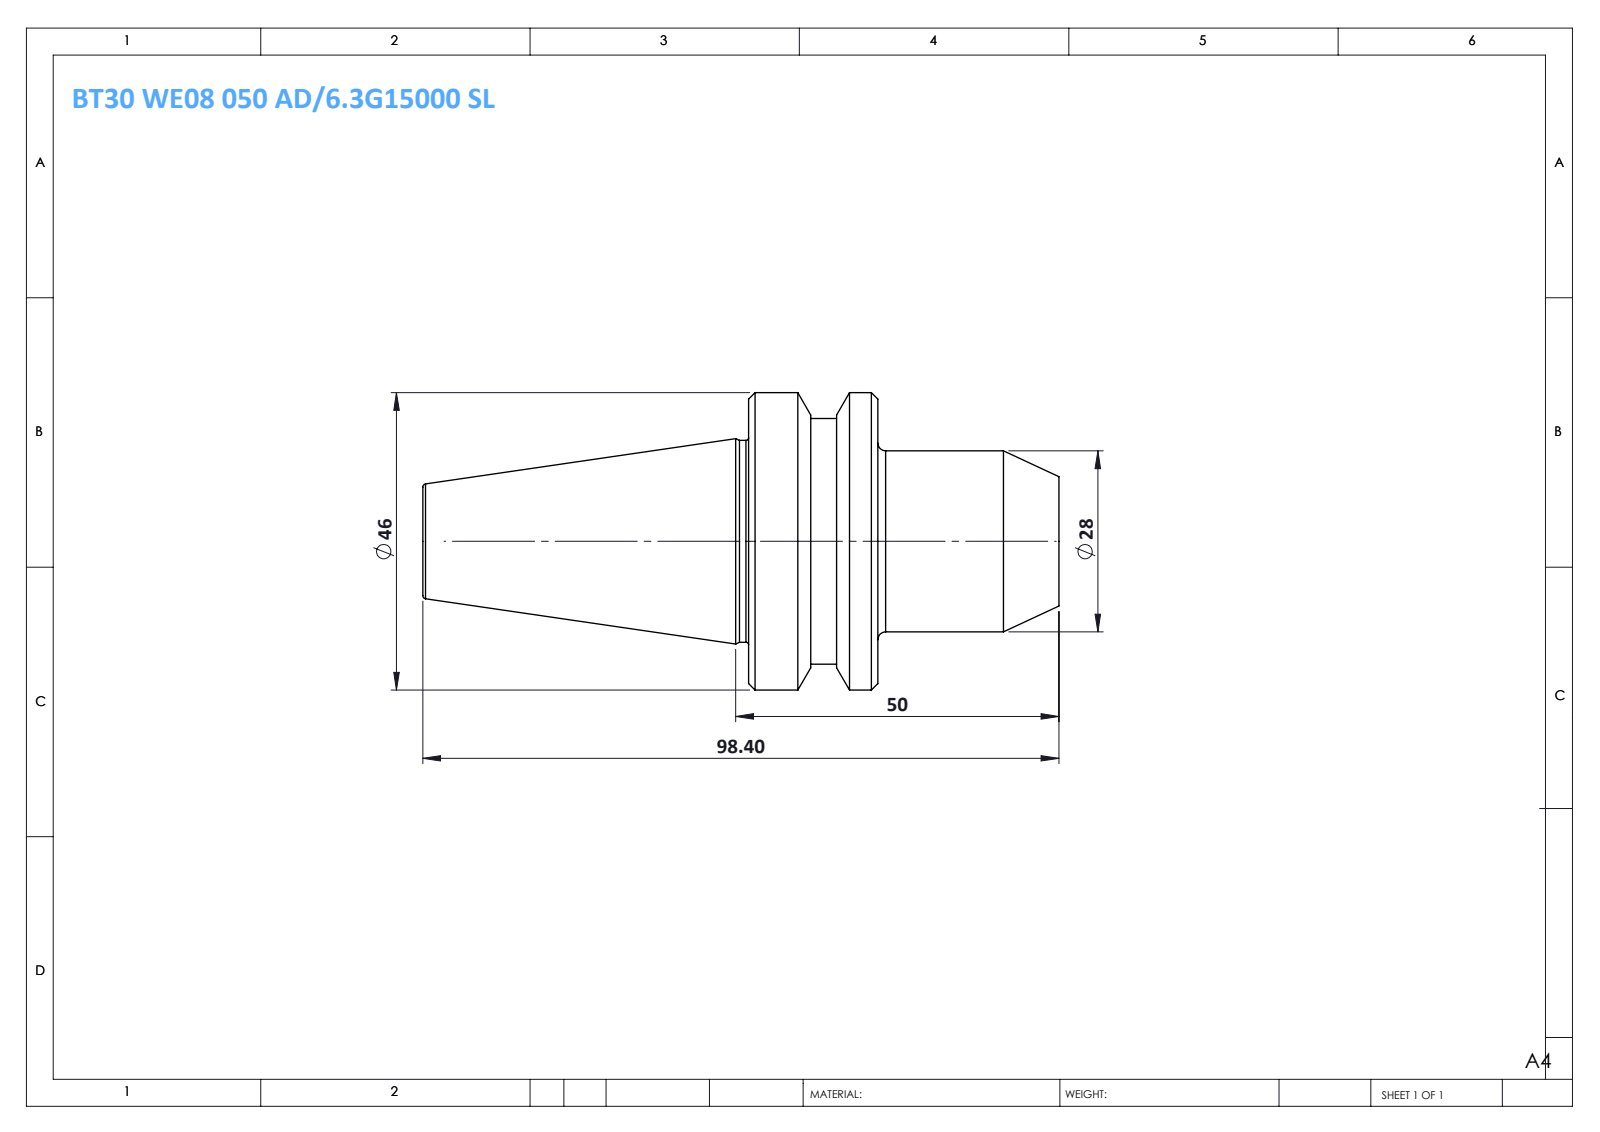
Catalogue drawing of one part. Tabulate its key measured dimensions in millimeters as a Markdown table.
| quantity | value |
| --- | --- |
| part name | BT30 WE08 050 AD-6.3G15000 SL |
| STEP written by | SolidWorks 2014 (CONFIG_CONTROL_DESIGN) |
| units | millimeters |
| bodies | 1 solid, 36 faces (6 planar, 10 cylindrical, 20 other) |
| overall size | 98.4 × 46 × 46 |
| volume | 71 282 mm³ |
| surface area | 12 089 mm² |
| round bosses / shafts (diameter × count) | 46 × 1, 38 × 1, 31.2 × 1, 28 × 1 |
| main face-to-face distances | 20, 28, 48, 98.4, 70.4, 50.4, 38.4, 10.4, 9.6, 60 |
